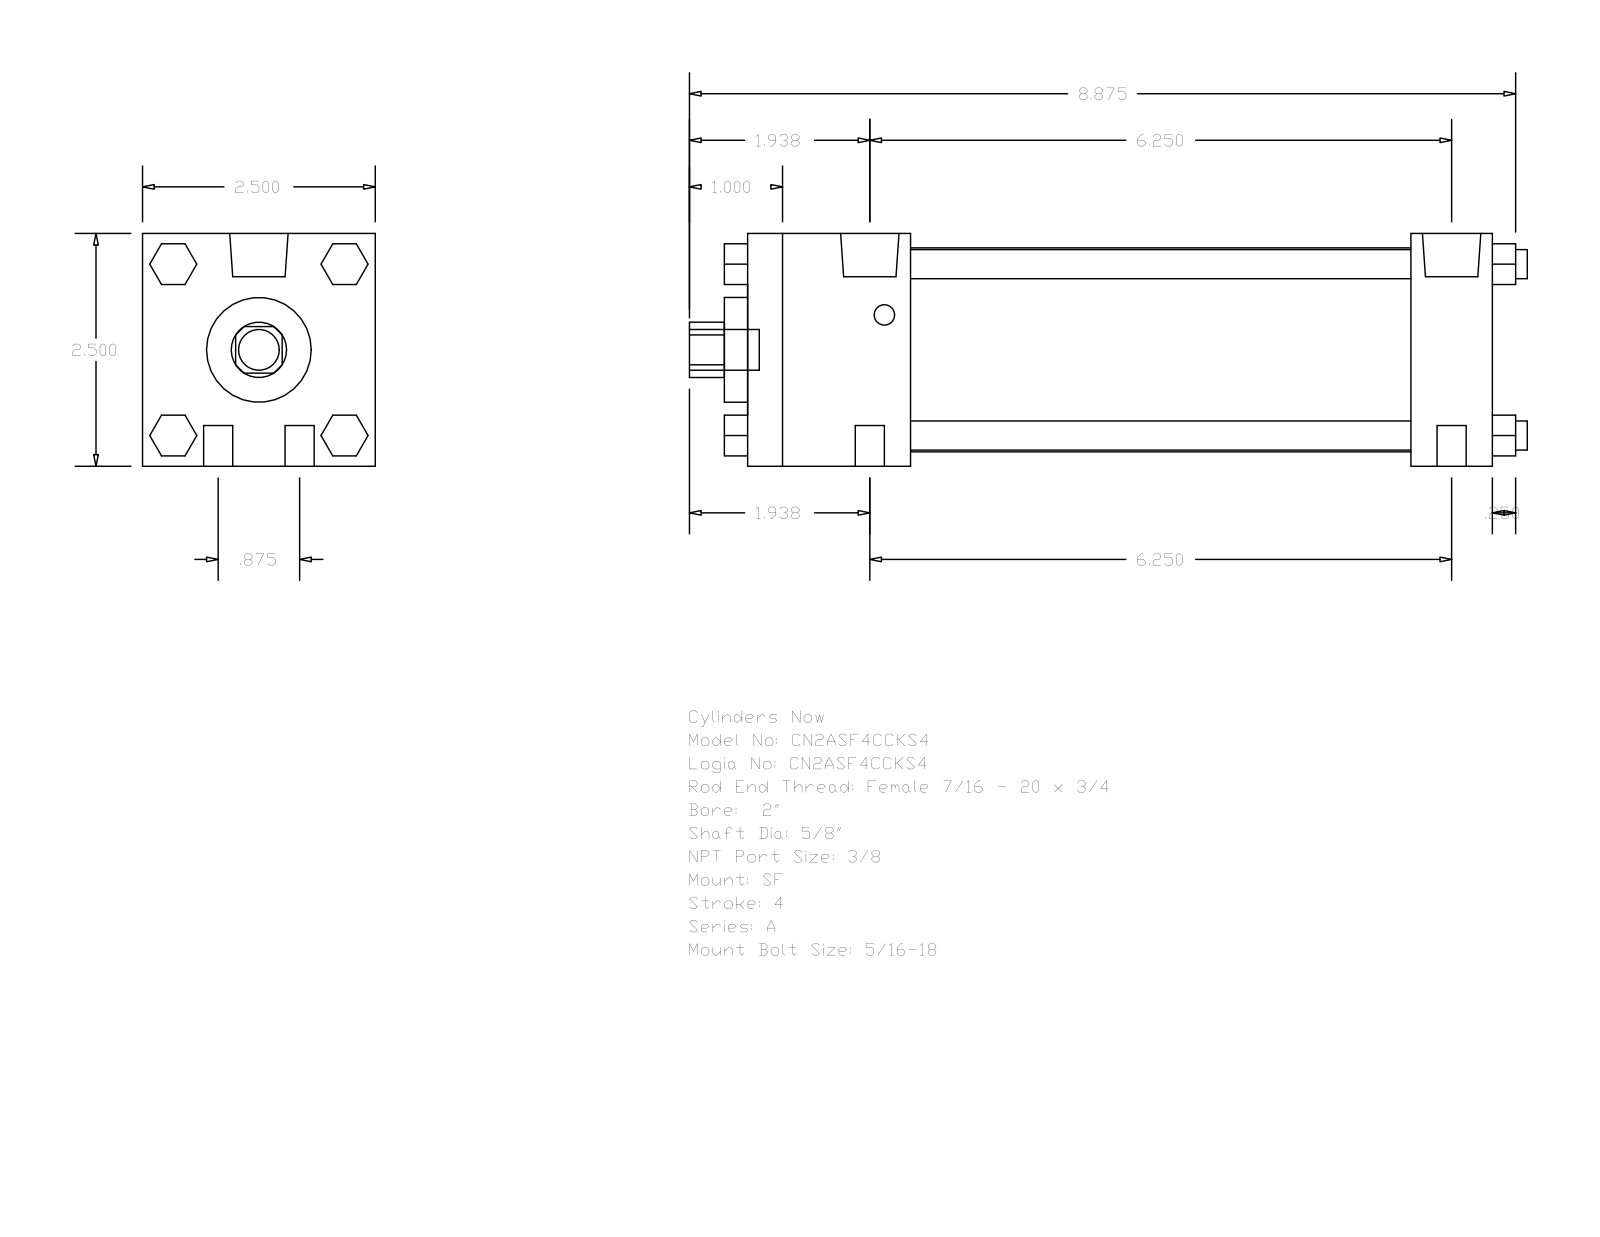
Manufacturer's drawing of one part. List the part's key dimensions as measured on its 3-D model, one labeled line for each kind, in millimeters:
Part name (STEP PRODUCT): A_SF__0200_0.625
STEP written by: GSSL Pune (CONFIG_CONTROL_DESIGN)
Units: millimetres
Bodies: 0 solids, 124 faces (94 planar, 30 cylindrical, 0 other)
Overall size (bounding box): 228.6 × 63.5 × 63.5
Round holes (diameter × count): ⌀15.88 ×1, ⌀28.57 ×1, ⌀55.63 ×1
Round bosses / shafts (diameter × count): ⌀7.94 ×8, ⌀15.93 ×2, ⌀5.56 ×2, ⌀11.11 ×1
Partial cylindrical surfaces — rounded edges, fillets, slot ends (radius × count): R7.54 ×1
Main face-to-face distances: 63.5, 203.19, 180.97, 22.22, 44.45, 136.52, 158.74, 50.8, 6.35, 187.32
